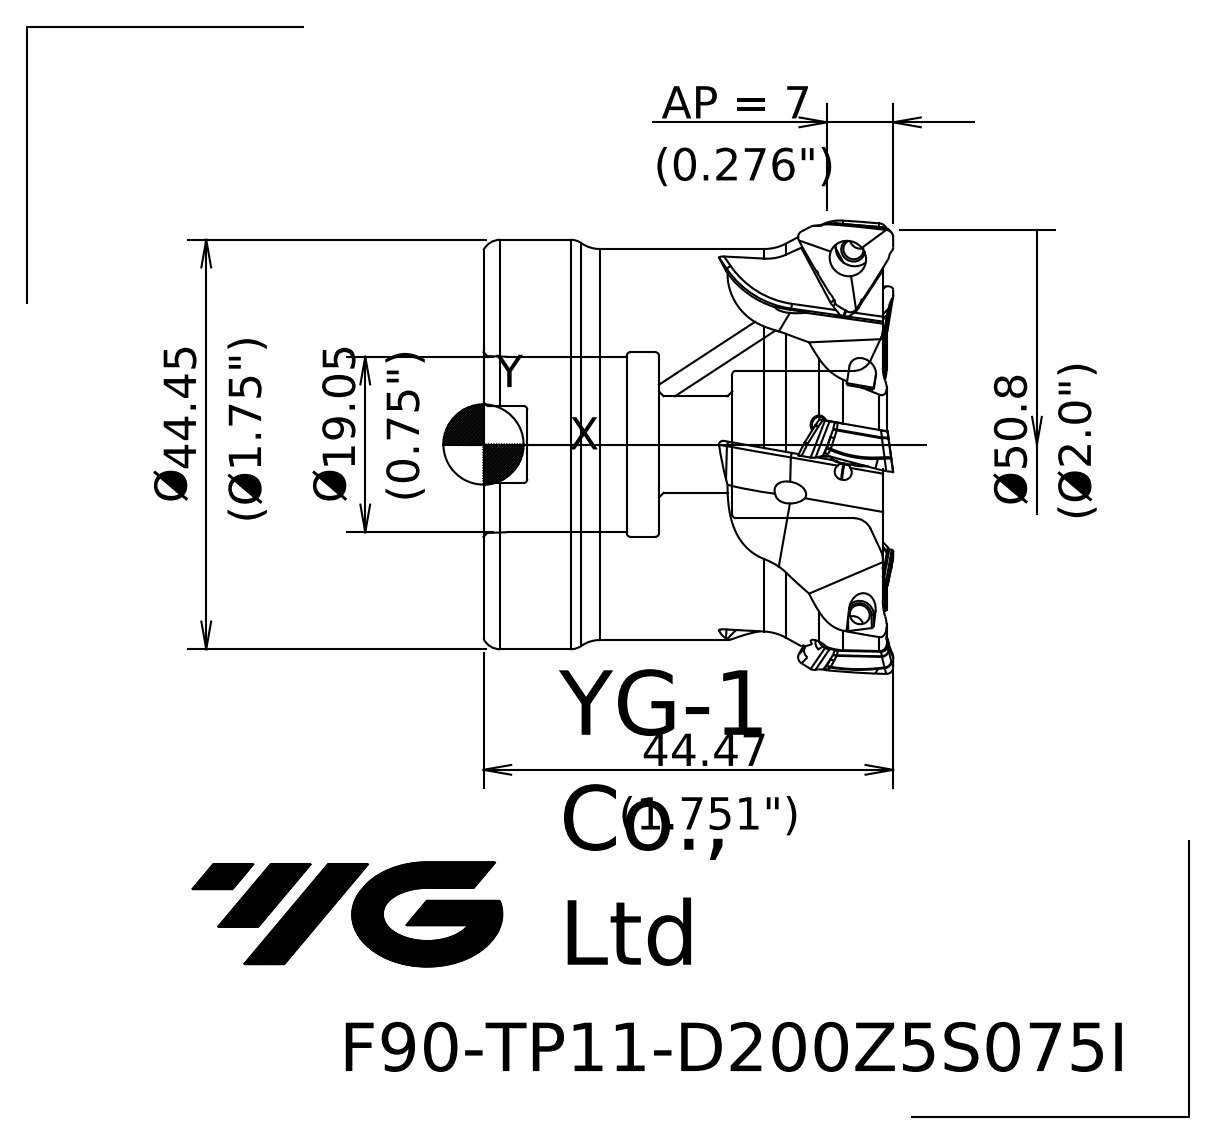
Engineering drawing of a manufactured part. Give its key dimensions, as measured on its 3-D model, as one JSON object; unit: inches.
{"part_name": "10225314C5E0pbw1", "step_written_by": "SIEMENS PLM Software NX 10.0 (AP203_CONFIGURATION_CONTROLLED_3D_DESIGN_OF_MECHANICAL_PARTS_AND_ASSEMBLIES_MIM_LF)", "units": "inches", "bodies": {"solids": 2, "faces": 171, "planar": 34, "cylindrical": 39, "other": 98}, "overall_size": [2.004, 2.004, 1.751], "volume_in3": 3.381, "surface_area_in2": 26.42, "round_holes": [[0.079, 5], [0.094, 5], [0.158, 1], [0.413, 1], [0.63, 1], [0.75, 1], [0.789, 1]], "round_bosses_or_shafts": [[1.75, 1], [1.671, 1]], "partial_cylinders_radius": [[0.031, 6], [0.035, 6], [0.055, 3], [0.059, 3], [0.016, 2]], "face_to_face_distances": [1.707, 1.52, 0.187, 0.957, 0.563, 0.75, 0.329, 0.644, 0.313, 0.876]}
